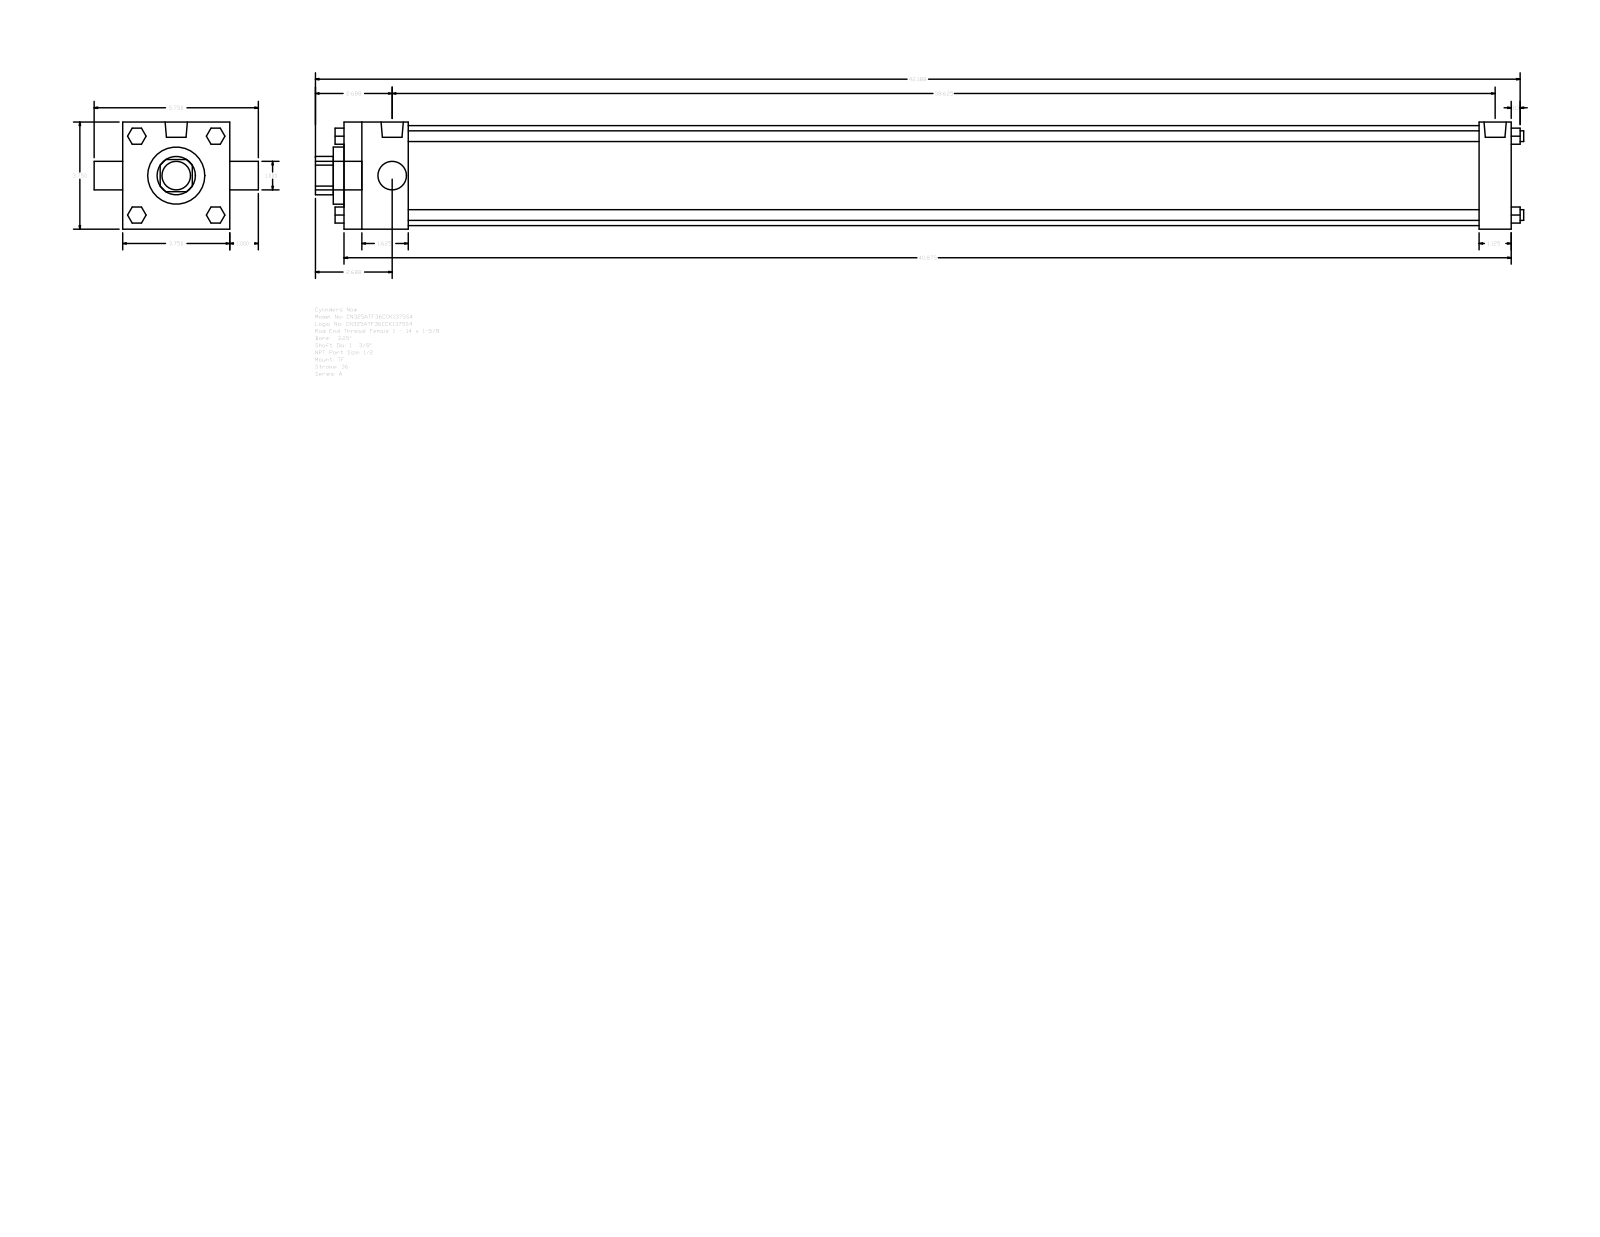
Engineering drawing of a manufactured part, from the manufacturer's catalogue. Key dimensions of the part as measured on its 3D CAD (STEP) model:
Part name (STEP PRODUCT): A_TF__0325_1.375
STEP written by: GSSL Pune (CONFIG_CONTROL_DESIGN)
Units: millimetres
Bodies: 0 solids, 120 faces (92 planar, 28 cylindrical, 0 other)
Overall size (bounding box): 1074.74 × 146.05 × 95.25
Round holes (diameter × count): ⌀25.4 ×1, ⌀34.92 ×1, ⌀50.8 ×1, ⌀88.9 ×1
Round bosses / shafts (diameter × count): ⌀9.53 ×4, ⌀8.73 ×3, ⌀19.77 ×2, ⌀25.4 ×1
Partial cylindrical surfaces — rounded edges, fillets, slot ends (radius × count): R17.06 ×1
Main face-to-face distances: 95.24, 1038.22, 28.57, 57.15, 1009.65, 952.5, 981.07, 9.52, 66.67, 1019.17
